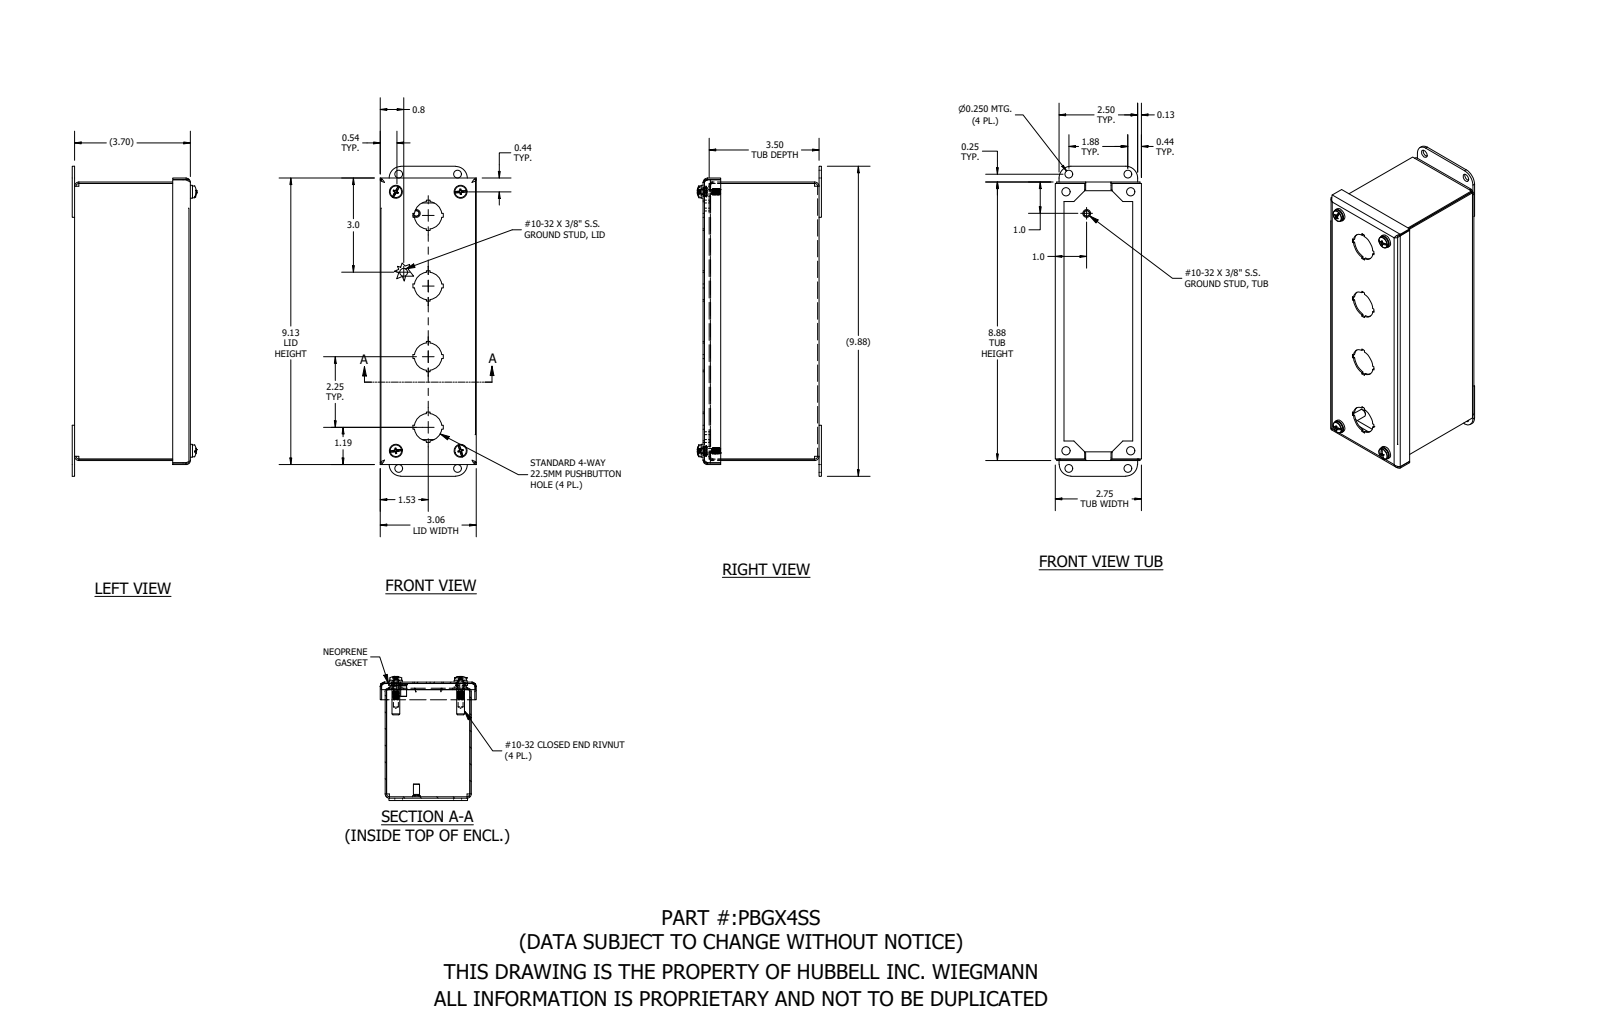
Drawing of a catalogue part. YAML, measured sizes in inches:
part_name: "PBGX4SS"
step_written_by: "SolidWorks 2021 (AUTOMOTIVE_DESIGN)"
units: inches
bodies: {solids: 20, faces: 776, planar: 364, cylindrical: 260, other: 152}
overall_size: [9.875, 3.954, 3.063]
volume: 9.524
surface_area: 352.7
round_holes:
  - {diameter: 0.156, count: 4}
  - {diameter: 0.196, count: 4}
  - {diameter: 0.25, count: 4}
  - {diameter: 0.257, count: 4}
  - {diameter: 0.281, count: 4}
  - {diameter: 0.313, count: 4}
  - {diameter: 0.875, count: 4}
  - {diameter: 0.133, count: 2}
  - {diameter: 0.175, count: 2}
  - {diameter: 0.175, count: 2}
round_bosses_or_shafts:
  - {diameter: 0.406, count: 4}
  - {diameter: 0.318, count: 4}
  - {diameter: 0.248, count: 4}
  - {diameter: 0.186, count: 4}
  - {diameter: 0.141, count: 4}
  - {diameter: 0.14, count: 4}
  - {diameter: 0.375, count: 3}
  - {diameter: 0.25, count: 2}
partial_cylinders:
  - {radius: 0.094, count: 8}
  - {radius: 0.139, count: 8}
  - {radius: 0.063, count: 4}
  - {radius: 0.108, count: 4}
  - {radius: 0.375, count: 4}
face_to_face_distances: [0.045, 0.045, 3.65, 2.705, 2.75, 2.66, 2.705, 3.695, 3.605, 0.156]
hole_center_spacings: [1.275, 3.172, 5.35, 5.888, 7.57, 8.117, 8.813, 9.03]
